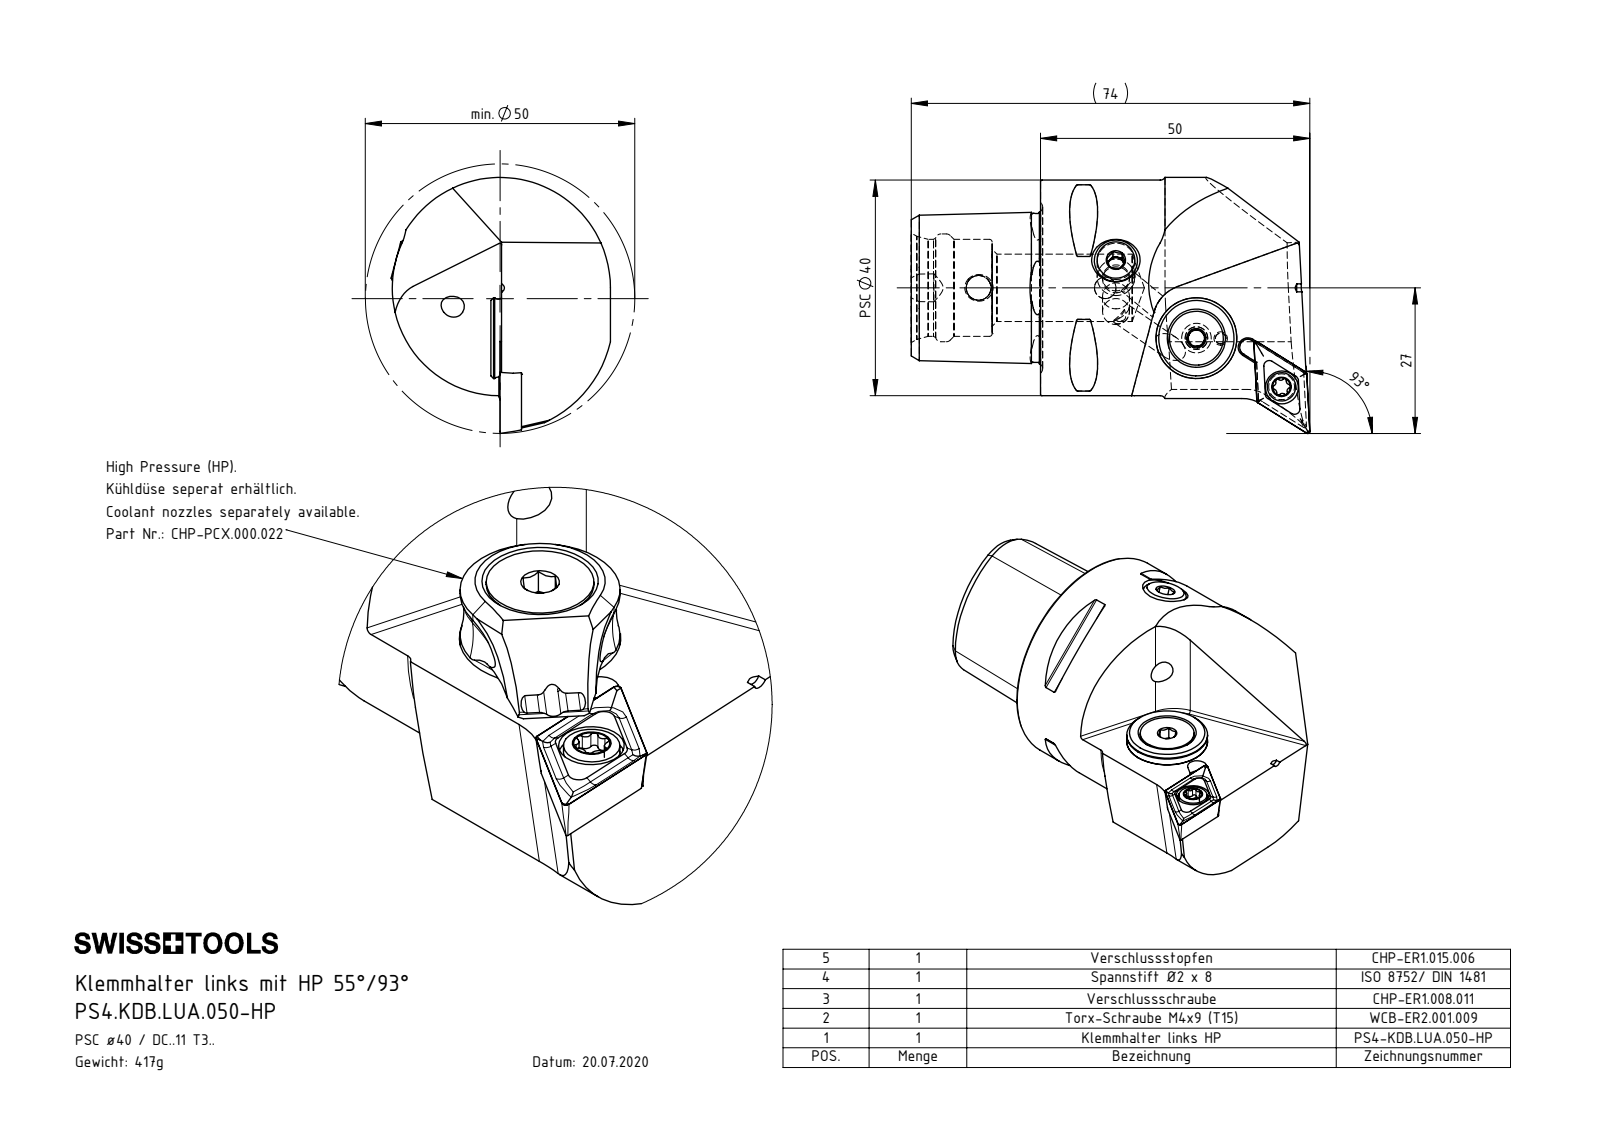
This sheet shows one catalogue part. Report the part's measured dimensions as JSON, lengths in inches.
{"part_name": "ISO 8752 2x8; CHP-ER1.015.006_A; DIN 7991 - M5x15; DCMT11T304 (+6 more)", "step_written_by": "SolidWorks 2017 (AUTOMOTIVE_DESIGN)", "units": "inches", "bodies": {"solids": 8, "faces": 390, "planar": 91, "cylindrical": 103, "other": 196}, "overall_size": [2.913, 1.87, 1.603], "volume_in3": 3.246, "surface_area_in2": 24.34, "round_holes": [[0.165, 3], [0.047, 1], [0.079, 1], [0.098, 1], [0.118, 1], [0.13, 1], [0.157, 1], [0.173, 1], [0.181, 1], [0.197, 1], [0.205, 1], [0.24, 1]], "round_bosses_or_shafts": [[1.575, 1], [0.591, 1], [0.528, 1], [0.394, 1], [0.315, 1], [0.217, 1], [0.207, 1], [0.197, 1]], "partial_cylinders_radius": [[0.012, 8], [0.013, 6], [0.023, 6], [0.02, 2], [0.276, 2], [0.031, 1], [0.059, 1], [0.118, 1]], "face_to_face_distances": [0.177, 0.618, 0.795, 0.945, 0.651, 0.033, 0.144, 0.611, 1.39, 0.591], "hole_center_spacings": [0.177, 0.568, 0.572, 0.717, 0.721, 0.761, 0.921, 0.925]}
